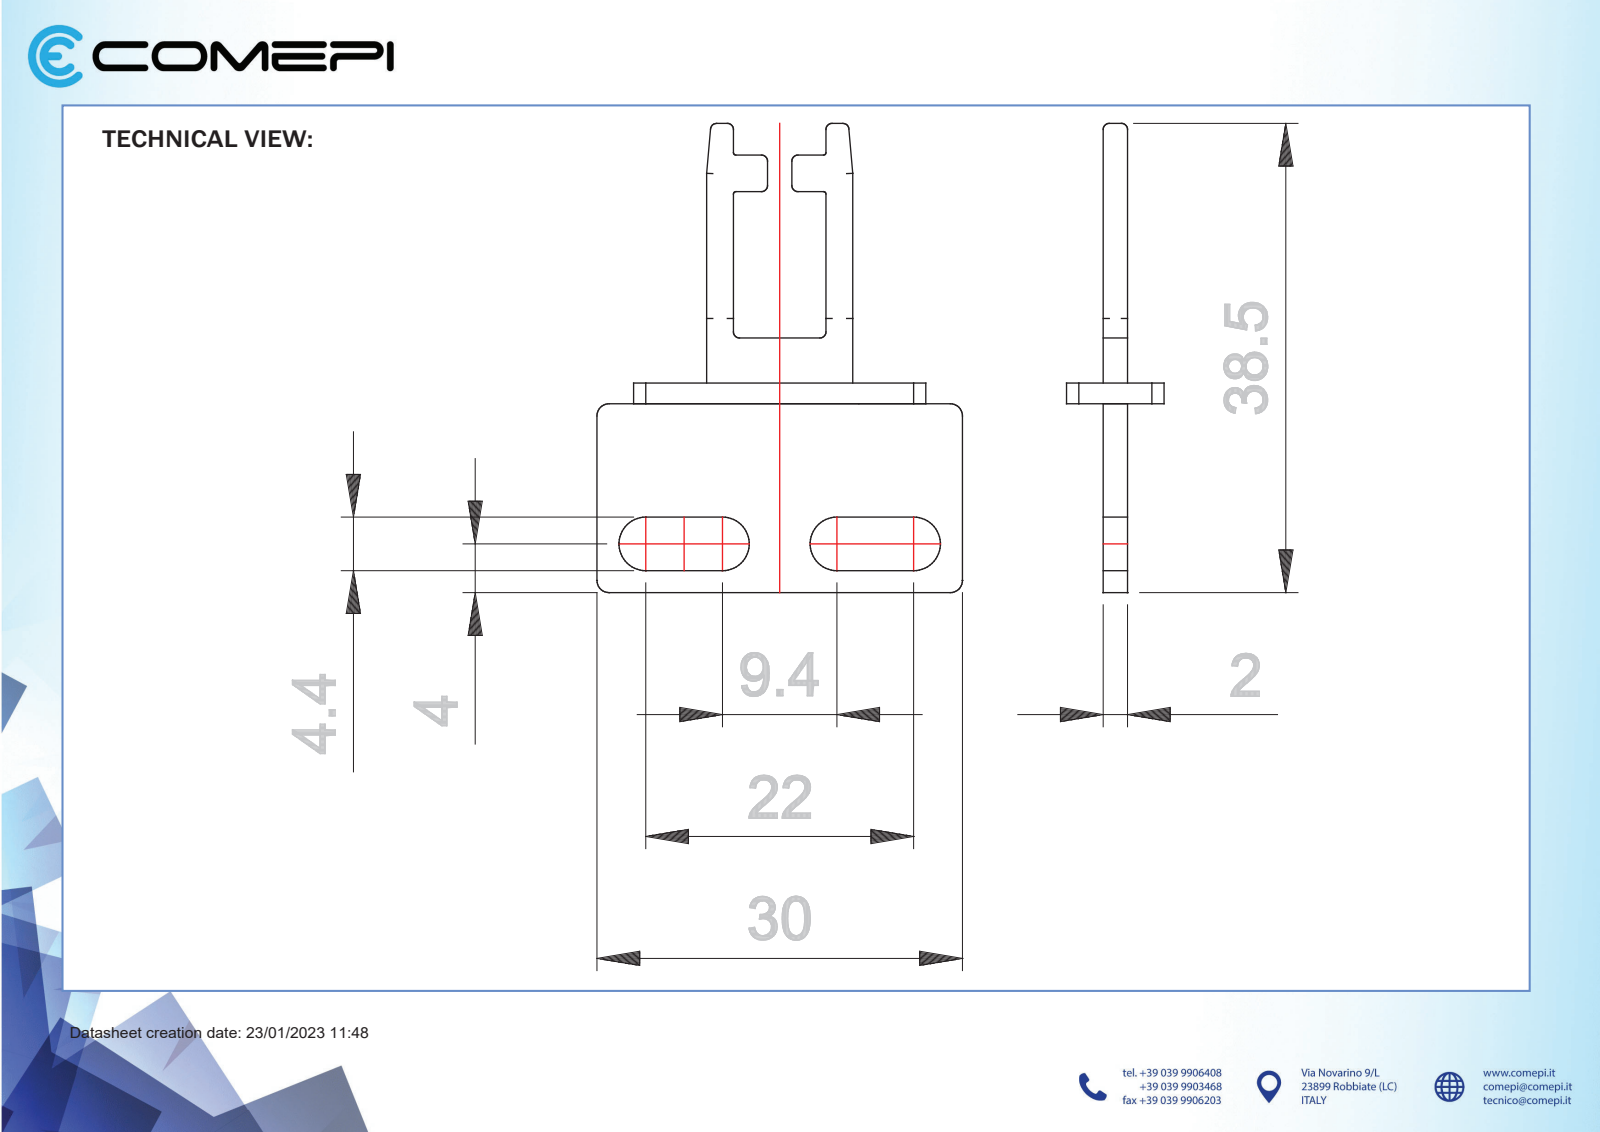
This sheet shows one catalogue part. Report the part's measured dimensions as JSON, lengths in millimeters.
{"part_name": "KEY4", "step_written_by": "SolidWorks 2021 (AUTOMOTIVE_DESIGN)", "units": "millimeters", "bodies": {"solids": 1, "faces": 63, "planar": 37, "cylindrical": 26, "other": 0}, "overall_size": [38.5, 30, 8], "volume_mm3": 1300, "surface_area_mm2": 1875, "partial_cylinders_radius": [[1, 8], [0.5, 6], [0.2, 4], [0.6, 4], [2.2, 4]], "face_to_face_distances": [2, 1.6, 3, 5, 18.8, 15.5, 17.1, 9, 21, 11.2]}
